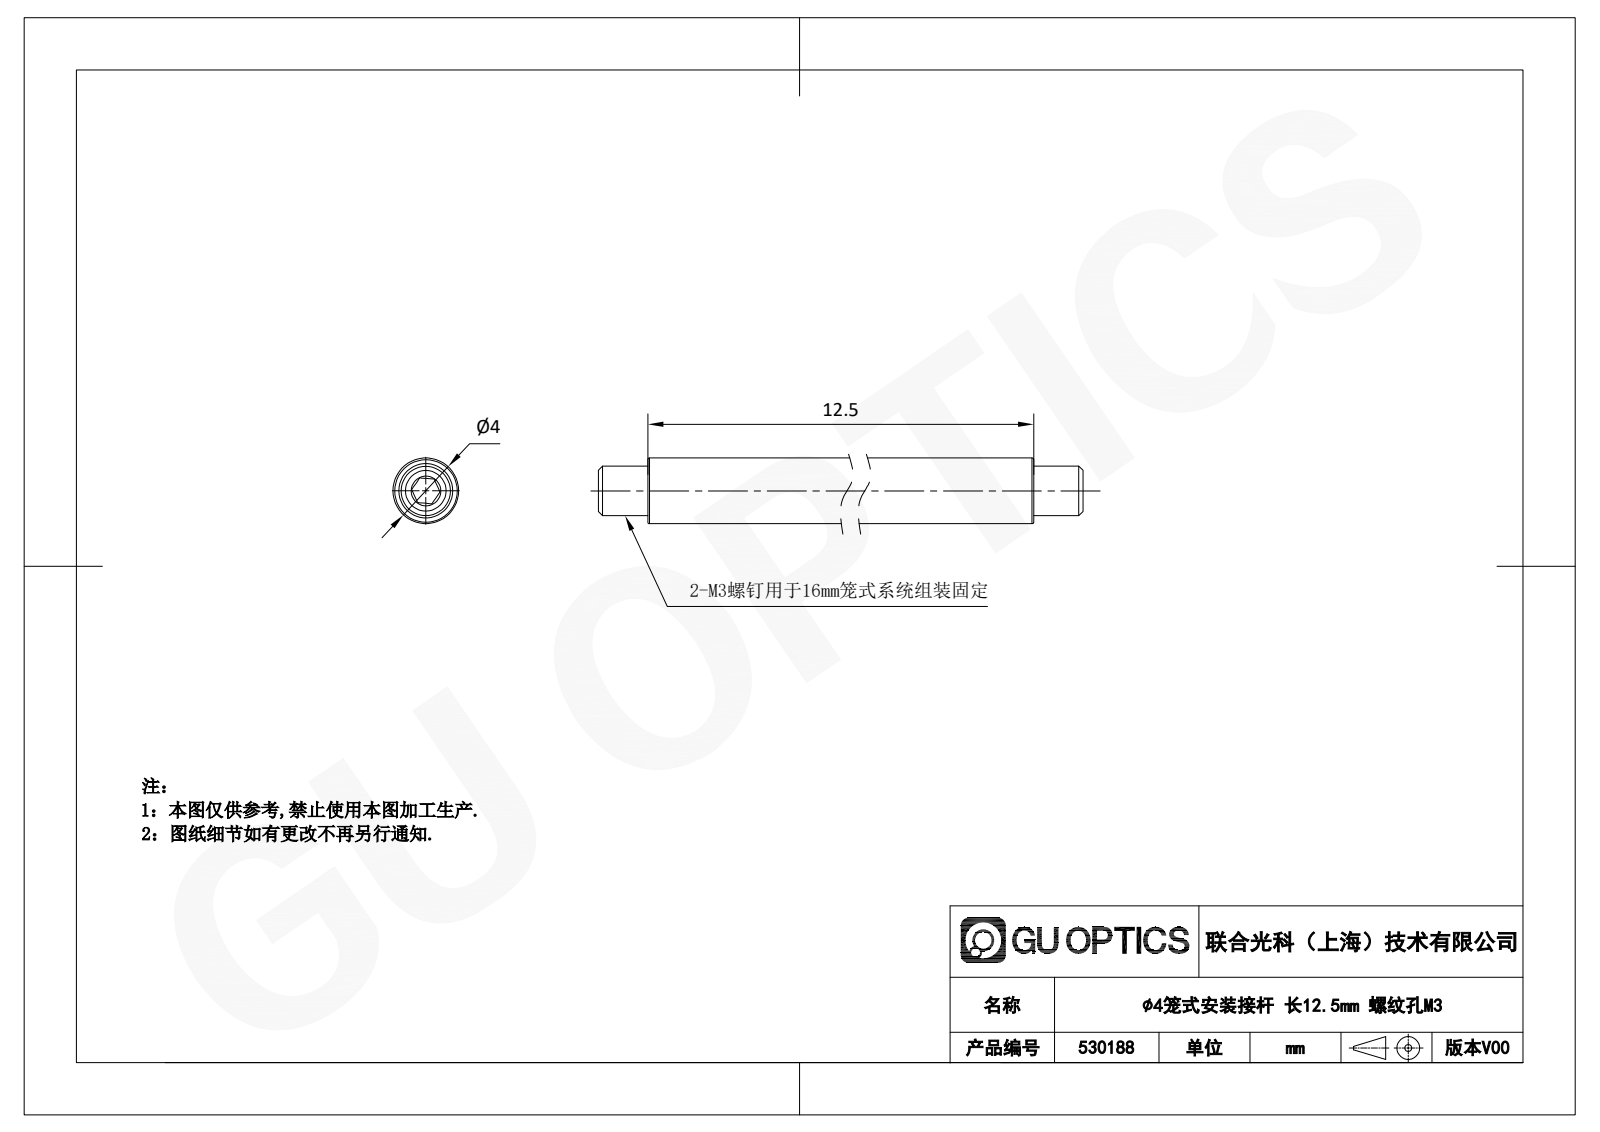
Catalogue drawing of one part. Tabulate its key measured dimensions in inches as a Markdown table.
| quantity | value |
| --- | --- |
| part name | 530188 |
| STEP written by | SolidWorks 2020 (CONFIG_CONTROL_DESIGN) |
| units | inches |
| bodies | 3 solids, 37 faces (20 planar, 5 cylindrical, 12 other) |
| overall size | 0.886 × 0.157 × 0.157 |
| volume | 0.013 in³ |
| surface area | 0.693 in² |
| round holes (diameter × count) | 0.098 × 1 |
| round bosses / shafts (diameter × count) | 0.157 × 1, 0.118 × 1 |
| main face-to-face distances | 0.118, 0.374, 0.197, 0.315, 0.571, 0.689, 0.059, 0.492, 0.039, 0.846 |
